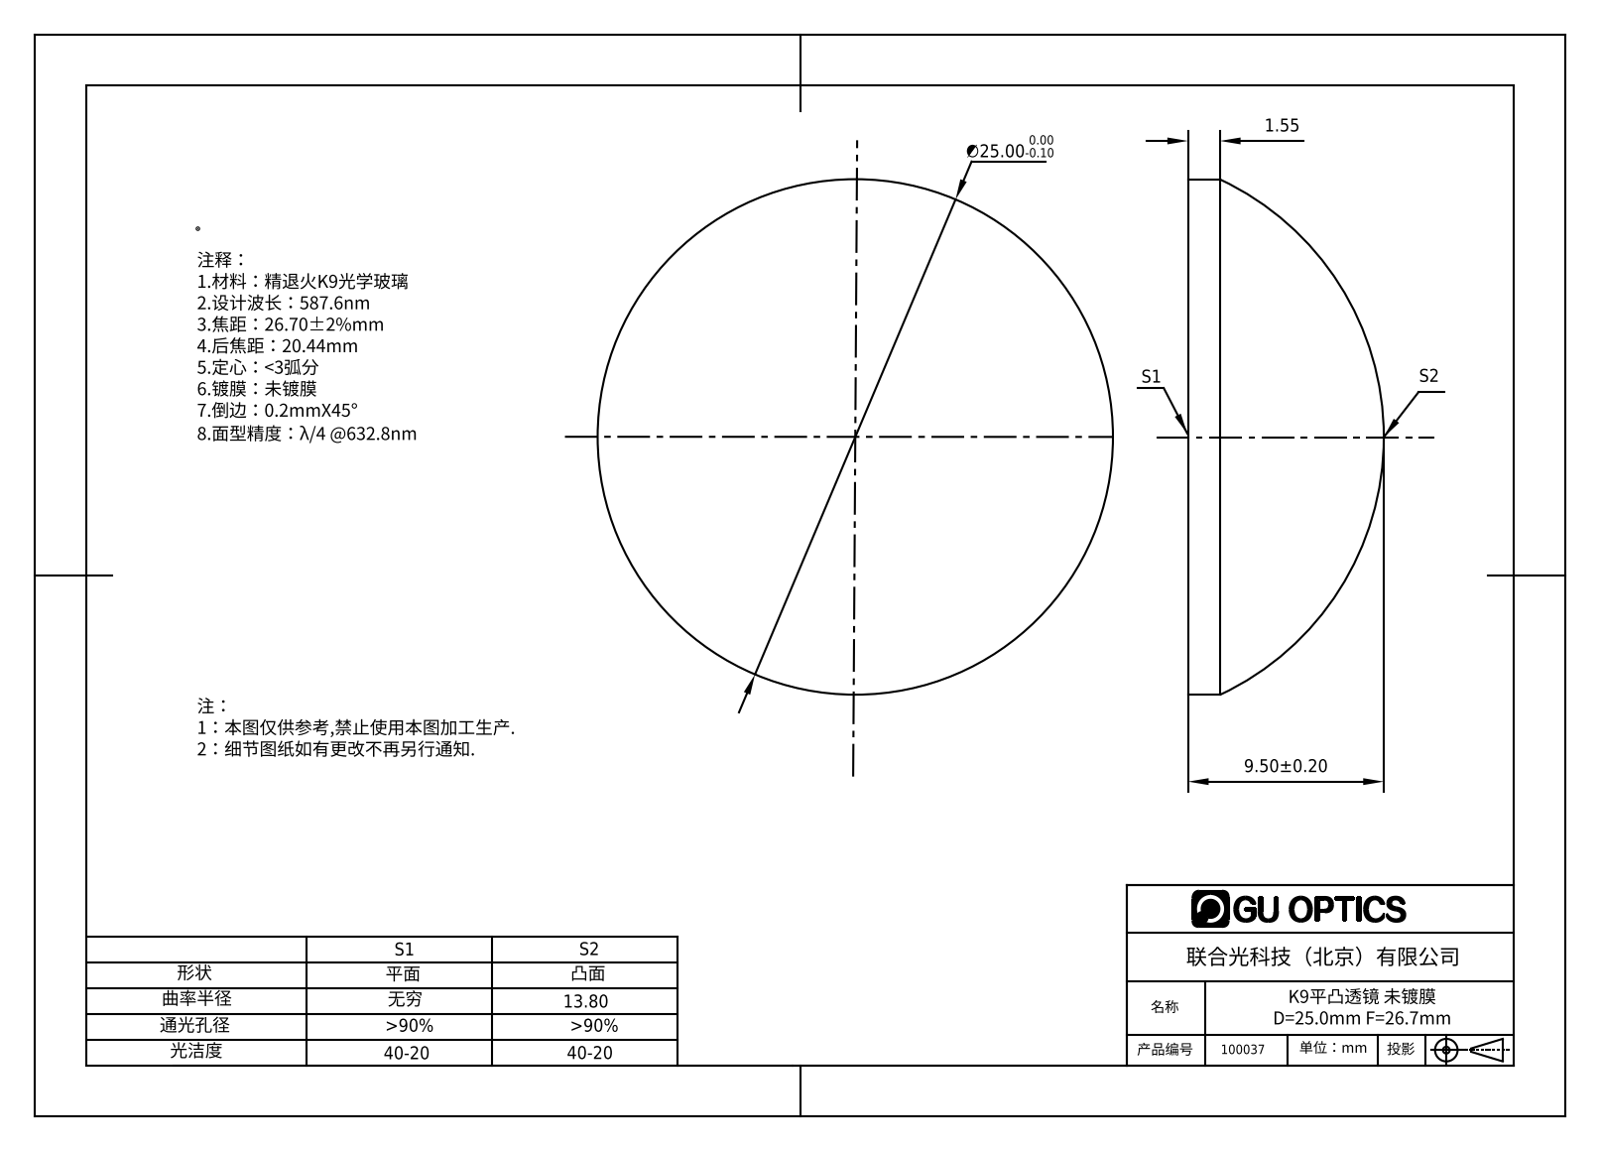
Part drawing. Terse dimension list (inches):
name: 100037
written by: SolidWorks 2016 (AUTOMOTIVE_DESIGN)
unit: in
bodies: 1 solid, 5 faces (1 planar, 2 cylindrical, 2 other)
size: 0.984 × 0.984 × 0.374
volume: 0.182 in³; area: 2.018 in²
bosses: 1× ⌀0.984
